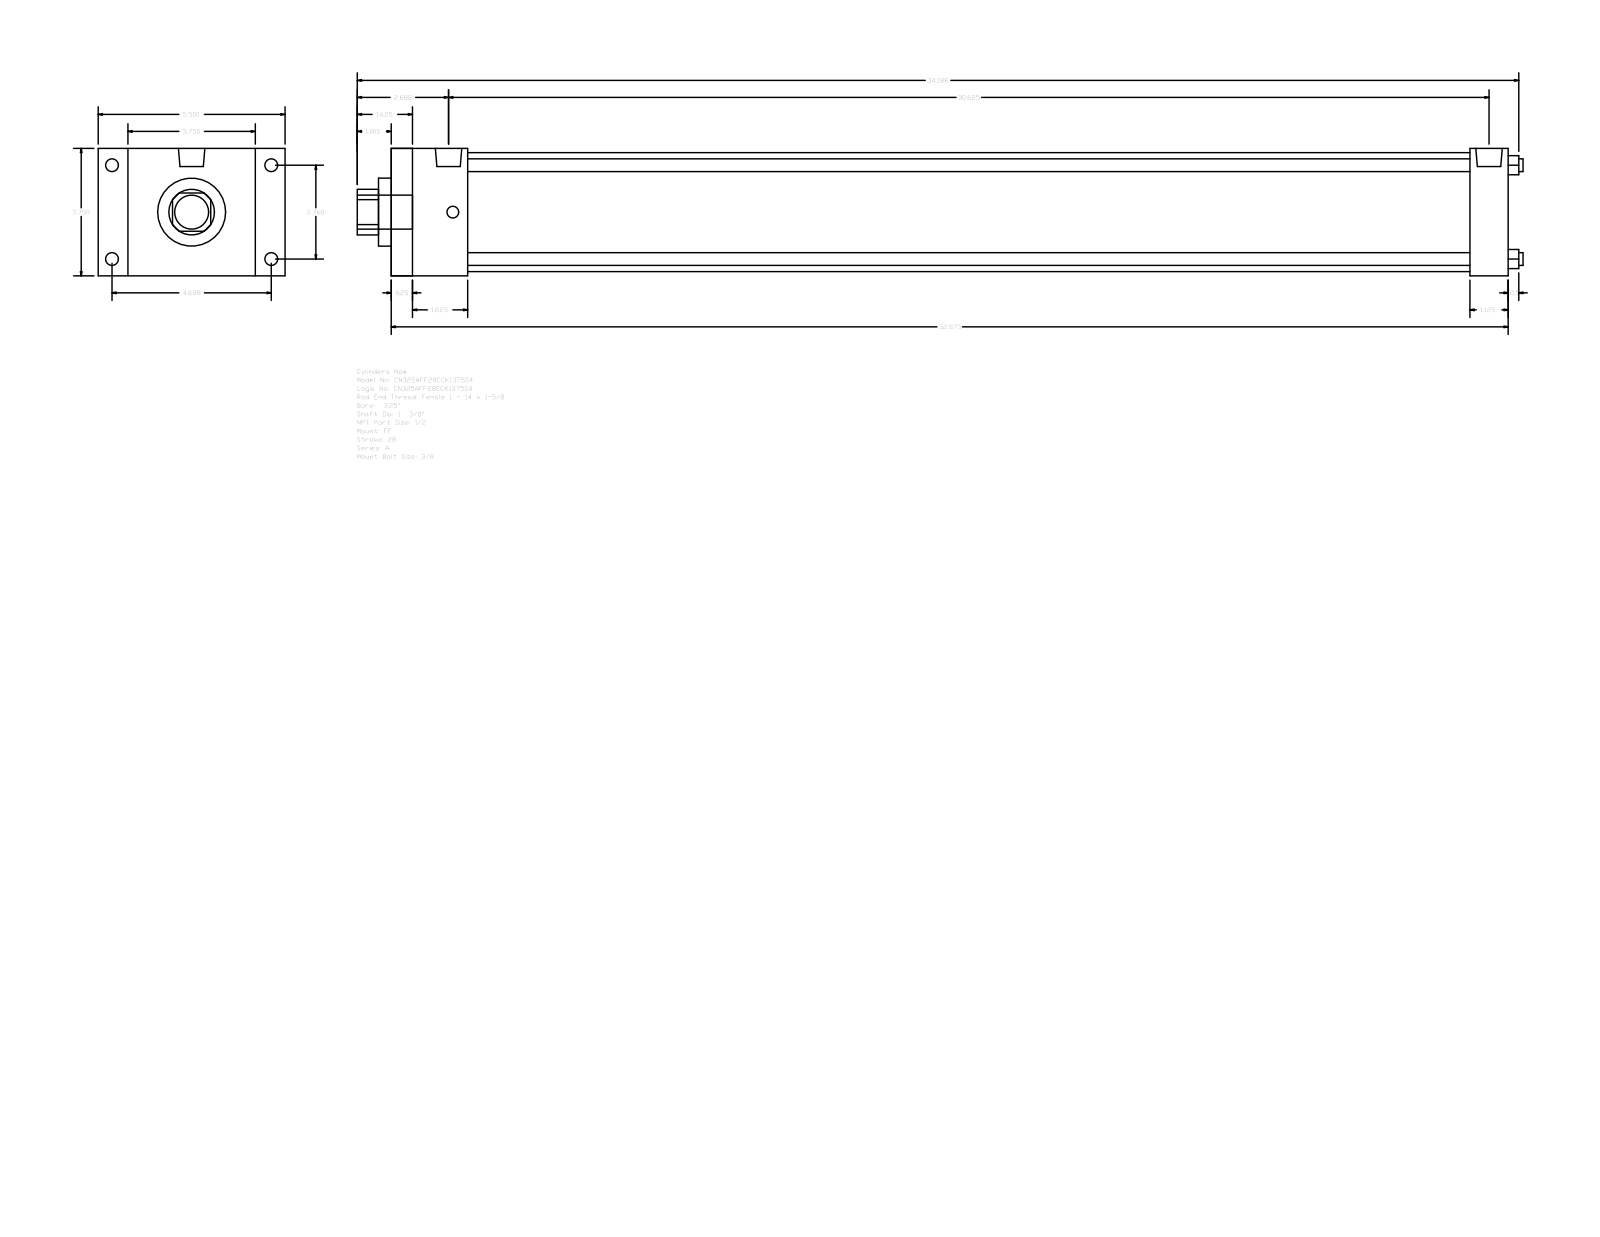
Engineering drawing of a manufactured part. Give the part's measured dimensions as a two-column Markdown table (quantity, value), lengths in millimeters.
| quantity | value |
| --- | --- |
| part name | A_FF__0325_1.375 |
| STEP written by | GSSL Pune (CONFIG_CONTROL_DESIGN) |
| units | millimeters |
| bodies | 0 solids, 92 faces (64 planar, 28 cylindrical, 0 other) |
| overall size | 871.54 × 139.7 × 95.25 |
| round holes (diameter × count) | 9.53 × 4, 34.92 × 1, 50.8 × 1, 88.9 × 1 |
| round bosses / shafts (diameter × count) | 9.53 × 4, 8.73 × 4, 19.77 × 2, 25.4 × 1 |
| partial cylindrical surfaces (radius × count) | 17.06 × 1 |
| main face-to-face distances | 95.24, 835.02, 819.15, 15.87, 22.23, 117.47, 28.57, 57.15, 806.45, 41.28 |
| hole center spacings | 49.57, 70.1, 99.14 |
